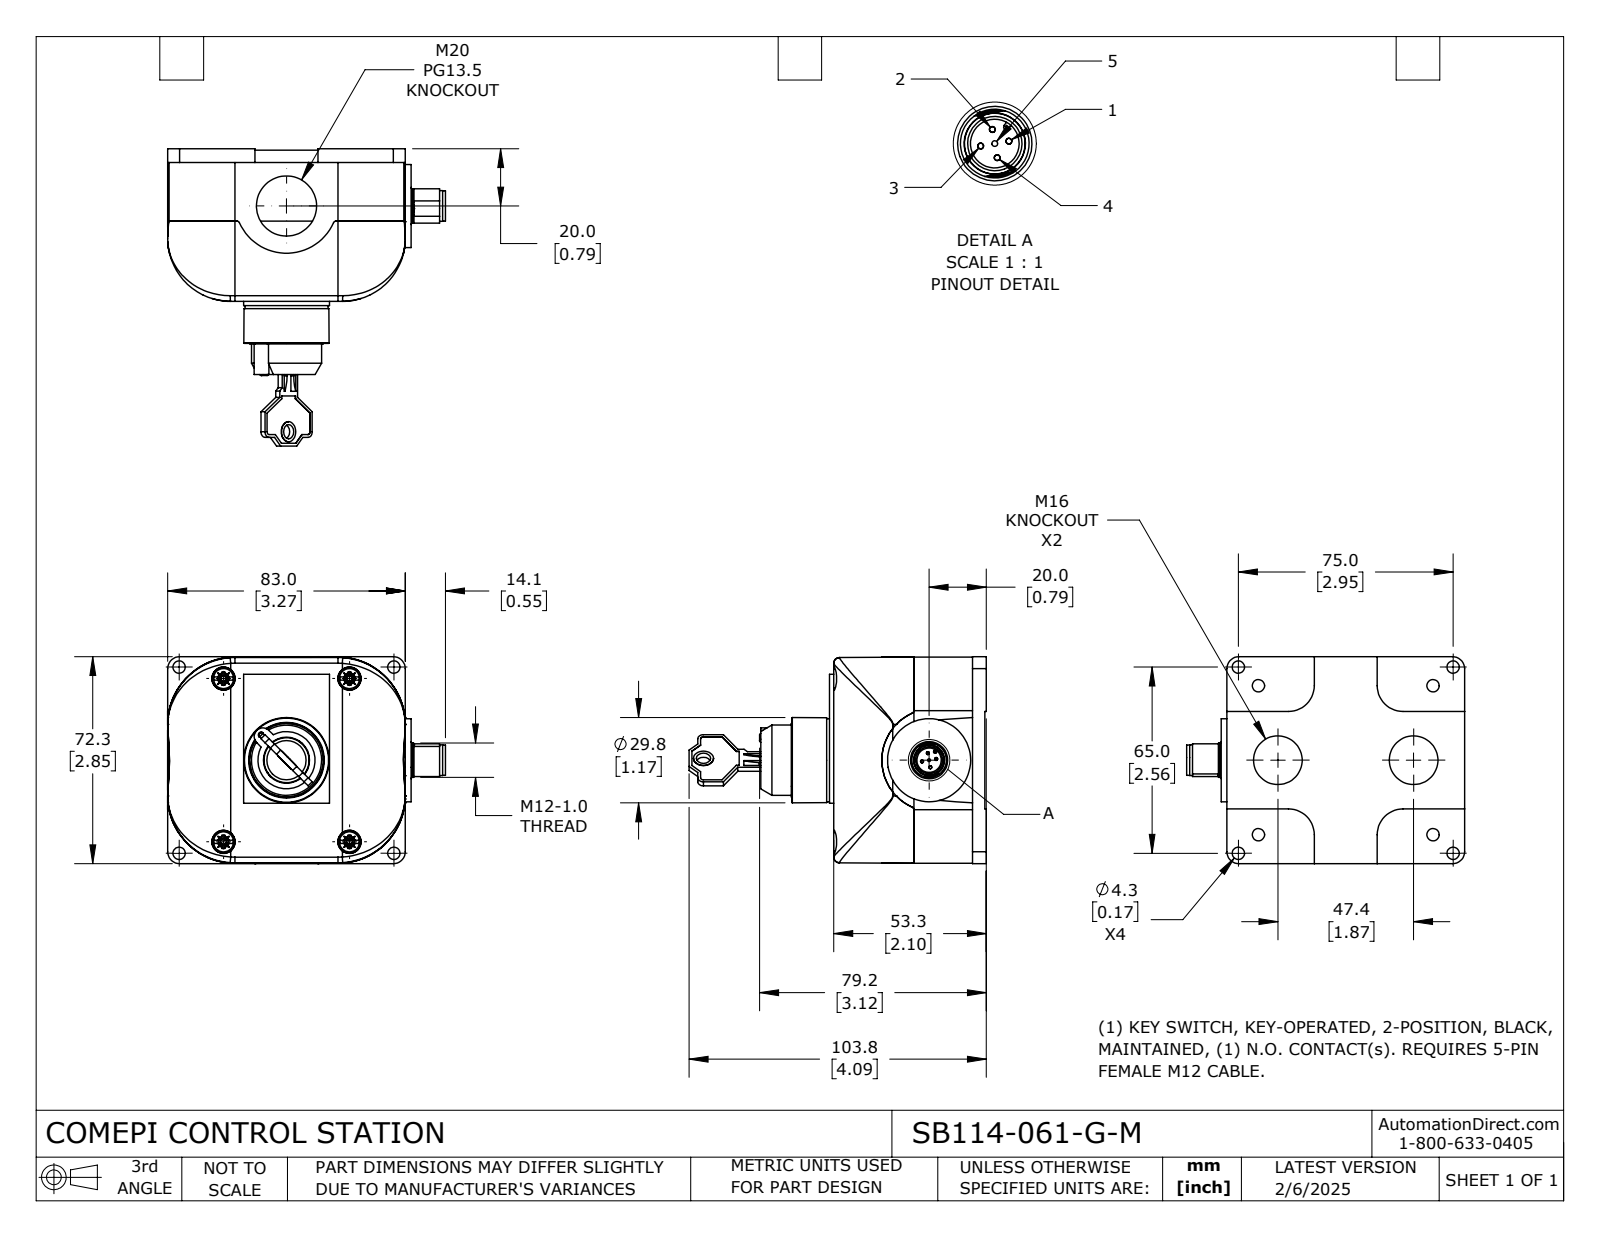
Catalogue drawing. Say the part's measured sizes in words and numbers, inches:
The part is named "SB114-061-G-M". Its 3-D file was written by "SolidWorks 2024 (CONFIG_CONTROL_DESIGN)". It is 11 solids with 929 faces: 479 planar, 312 cylindrical and 138 other. Overall it measures 4.087 by 3.821 by 2.846 inches. Its volume is 13.62 cubic inches and its surface area 104 square inches. Round holes: 8 of diameter 0.169, 4 of diameter 0.04, 4 of diameter 0.067, 4 of diameter 0.087, 4 of diameter 0.323, 2 of diameter 0.669, 2 of diameter 0.827, 1 of diameter 0.094, 1 of diameter 0.197, 1 of diameter 0.335, 1 of diameter 0.5, 1 of diameter 0.634. Round bosses or shafts: 5 of diameter 0.276, 5 of diameter 0.039, 4 of diameter 0.085, 4 of diameter 0.065, 2 of diameter 1.142, 2 of diameter 0.024, 1 of diameter 1.039, 1 of diameter 1.012. Partial cylindrical surfaces (rounded edges, fillets, slot ends): 8 of radius 0.039, 6 of radius 0.079, 5 of radius 0.02, 4 of radius 0.035, 4 of radius 0.354, 4 of radius 0.38, 4 of radius 0.925, 3 of radius 0.591. The main face-to-face distances are 2.079, 0.098, 0.976, 1.102, 0.878, 1.98, 0.118, 0.02, 0.996, 2.098. The hole center spacings are 0.376, 1.058, 1.39, 1.578, 1.954, 2.32, 2.367, 2.689.
